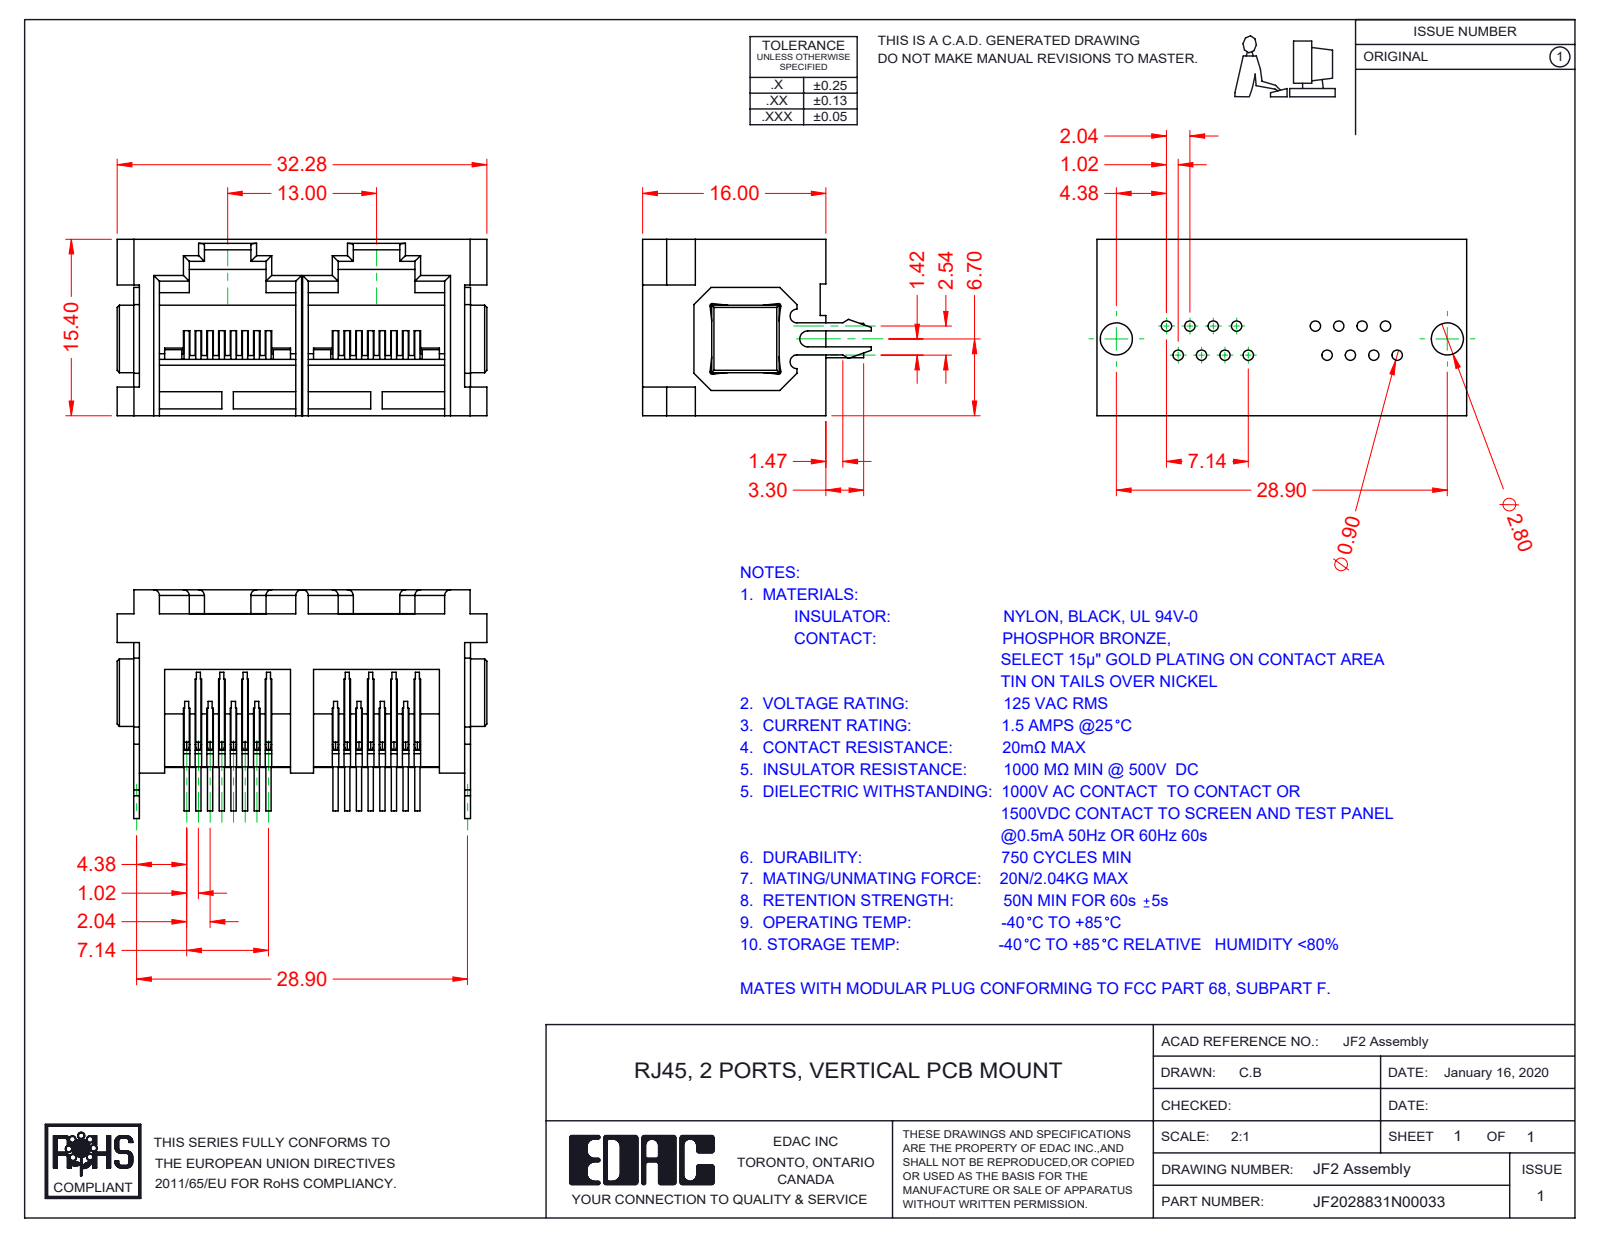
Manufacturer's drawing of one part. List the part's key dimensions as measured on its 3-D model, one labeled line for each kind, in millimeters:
Part name (STEP PRODUCT): F2 Insulator; F2 Boardlocks; RJF2028831N00033; F2 Contact Lock (+1 more)
STEP written by: SolidWorks 2016 (CONFIG_CONTROL_DESIGN)
Units: millimetres
Bodies: 21 solids, 1130 faces (734 planar, 300 cylindrical, 96 other)
Overall size (bounding box): 32.28 × 19.97 × 15.4
Volume: 3 519 mm³ · Surface area: 6 910 mm²
Round bosses / shafts (diameter × count): ⌀0.46 ×64
Partial cylindrical surfaces — rounded edges, fillets, slot ends (radius × count): R0.18 ×32, R0.5 ×15, R0.2 ×4, R20.35 ×4, R0.3 ×3, R0.6 ×2, R0.21 ×1, R0.45 ×1
Main face-to-face distances: 12.59, 2.1, 13, 1.5, 2.81, 0.92, 11.67, 0.5, 28.4, 11
